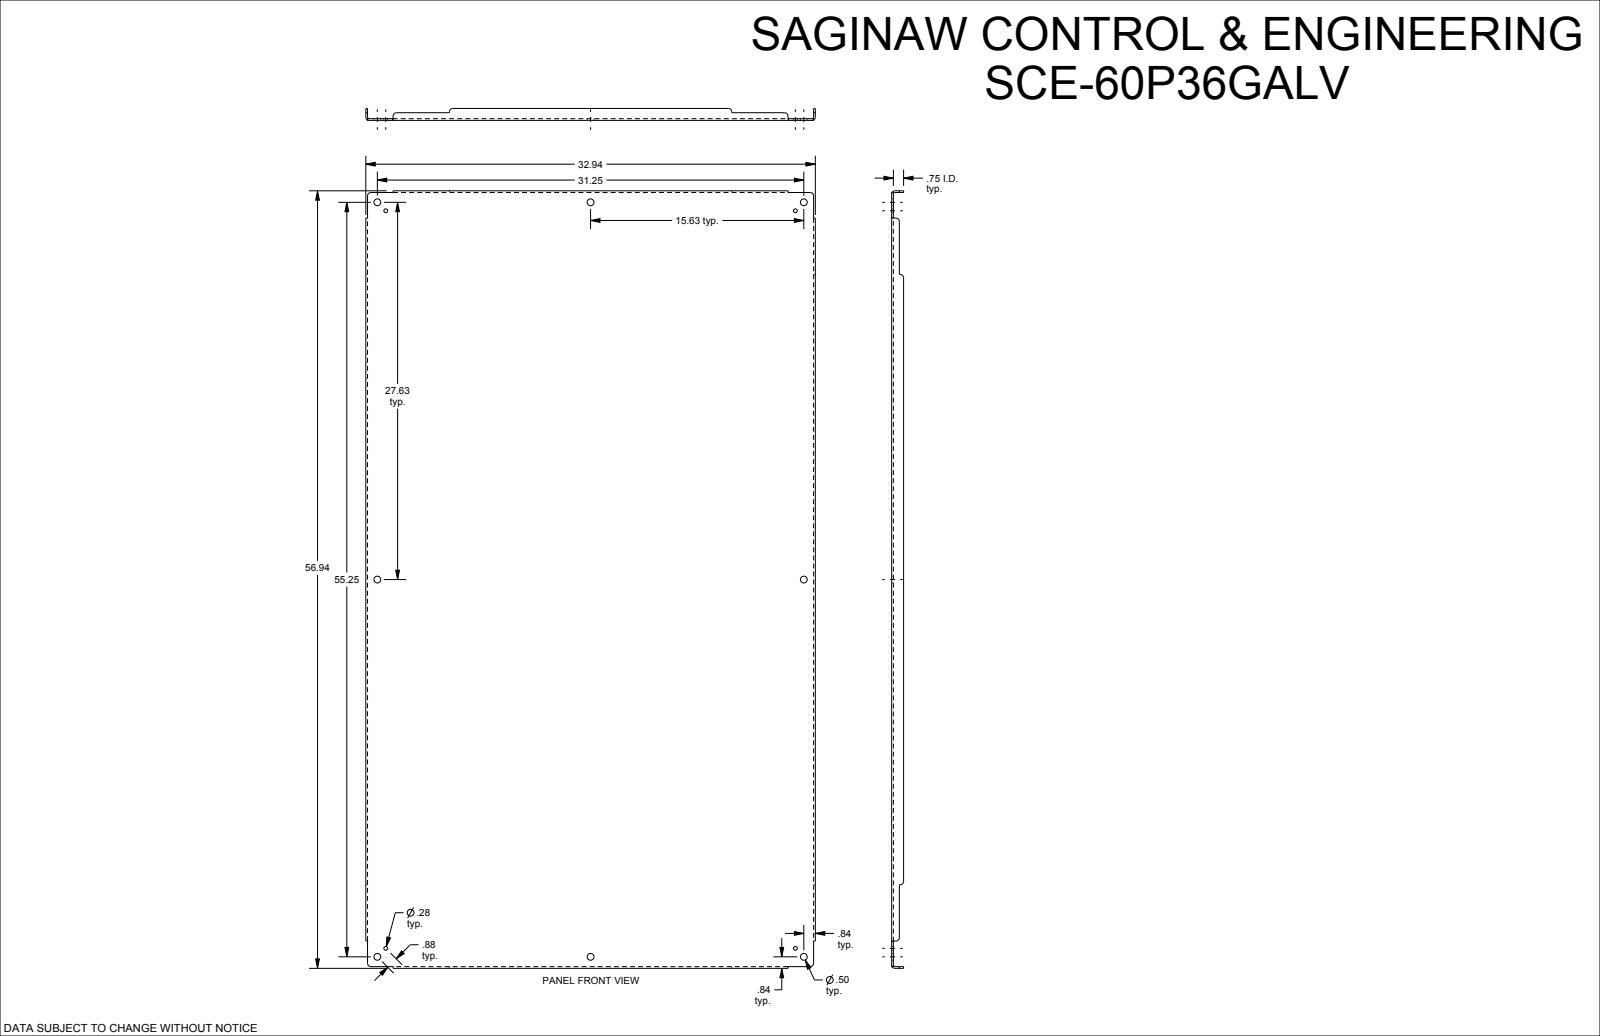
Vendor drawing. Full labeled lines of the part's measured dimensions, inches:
Part name (STEP PRODUCT): SCE-60P36GALV
STEP written by: SolidWorks 2019 (CONFIG_CONTROL_DESIGN)
Units: inches
Bodies: 1 solid, 110 faces (46 planar, 40 cylindrical, 24 other)
Overall size (bounding box): 56.938 × 32.938 × 0.875
Volume: 246.4 in³ · Surface area: 3 968 in²
Round holes (diameter × count): ⌀0.5 ×8, ⌀0.281 ×4
Partial cylindrical surfaces — rounded edges, fillets, slot ends (radius × count): R0.25 ×12, R0.112 ×4, R0.237 ×4
Main face-to-face distances: 0.125, 0.125, 32.813, 56.813, 32.687, 32.938, 56.687, 0.75, 0.875, 56.938
Hole centre spacings: 0.875, 15.019, 15.625, 27.013, 27.625, 30.638, 31.738, 40.837
